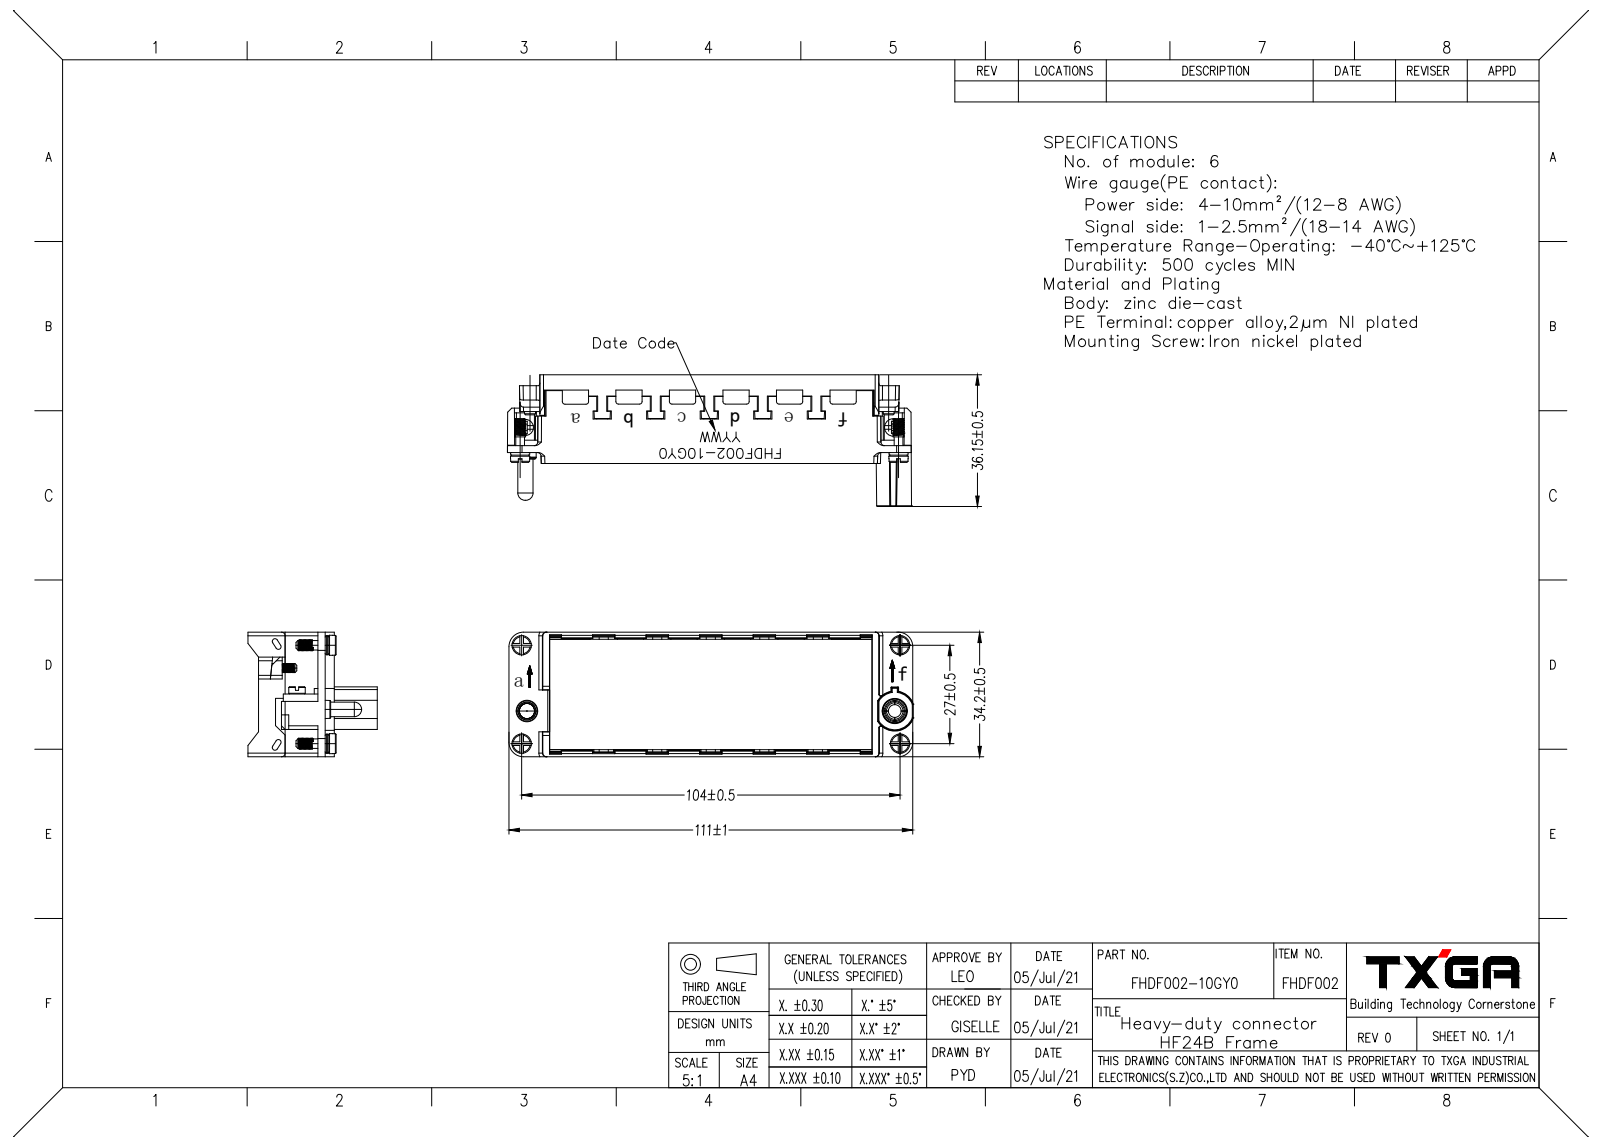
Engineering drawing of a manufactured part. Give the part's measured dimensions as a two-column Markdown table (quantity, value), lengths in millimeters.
| quantity | value |
| --- | --- |
| part name | FHDF002-10NA0 HF24B-NlA-REF（渲染） |
| STEP written by | SolidWorks 2021 (CONFIG_CONTROL_DESIGN) |
| units | millimeters |
| bodies | 1 solid, 1217 faces (644 planar, 387 cylindrical, 186 other) |
| overall size | 111 × 35.5 × 34.2 |
| volume | 13 326 mm³ |
| surface area | 17 658 mm² |
| round holes (diameter × count) | 3 × 4, 3.2 × 4, 4.36 × 2, 4.69 × 1, 6.5 × 1 |
| round bosses / shafts (diameter × count) | 5.5 × 4, 5.2 × 4, 2.6 × 4, 2.5 × 4, 4.53 × 2, 5.69 × 1, 4 × 1 |
| partial cylindrical surfaces (radius × count) | 1 × 28, 0.5 × 14, 0.4 × 4, 0.74 × 4, 5 × 4, 3.46 × 2, 3.5 × 2, 4 × 2 |
| main face-to-face distances | 1.75, 32.45, 34.2, 30.7, 2.3, 90.7, 31.3, 0.6, 88.4, 2 |
| hole center spacings | 9.5, 17.66, 27, 103.03, 104, 104.1, 107.45, 101.2 |
